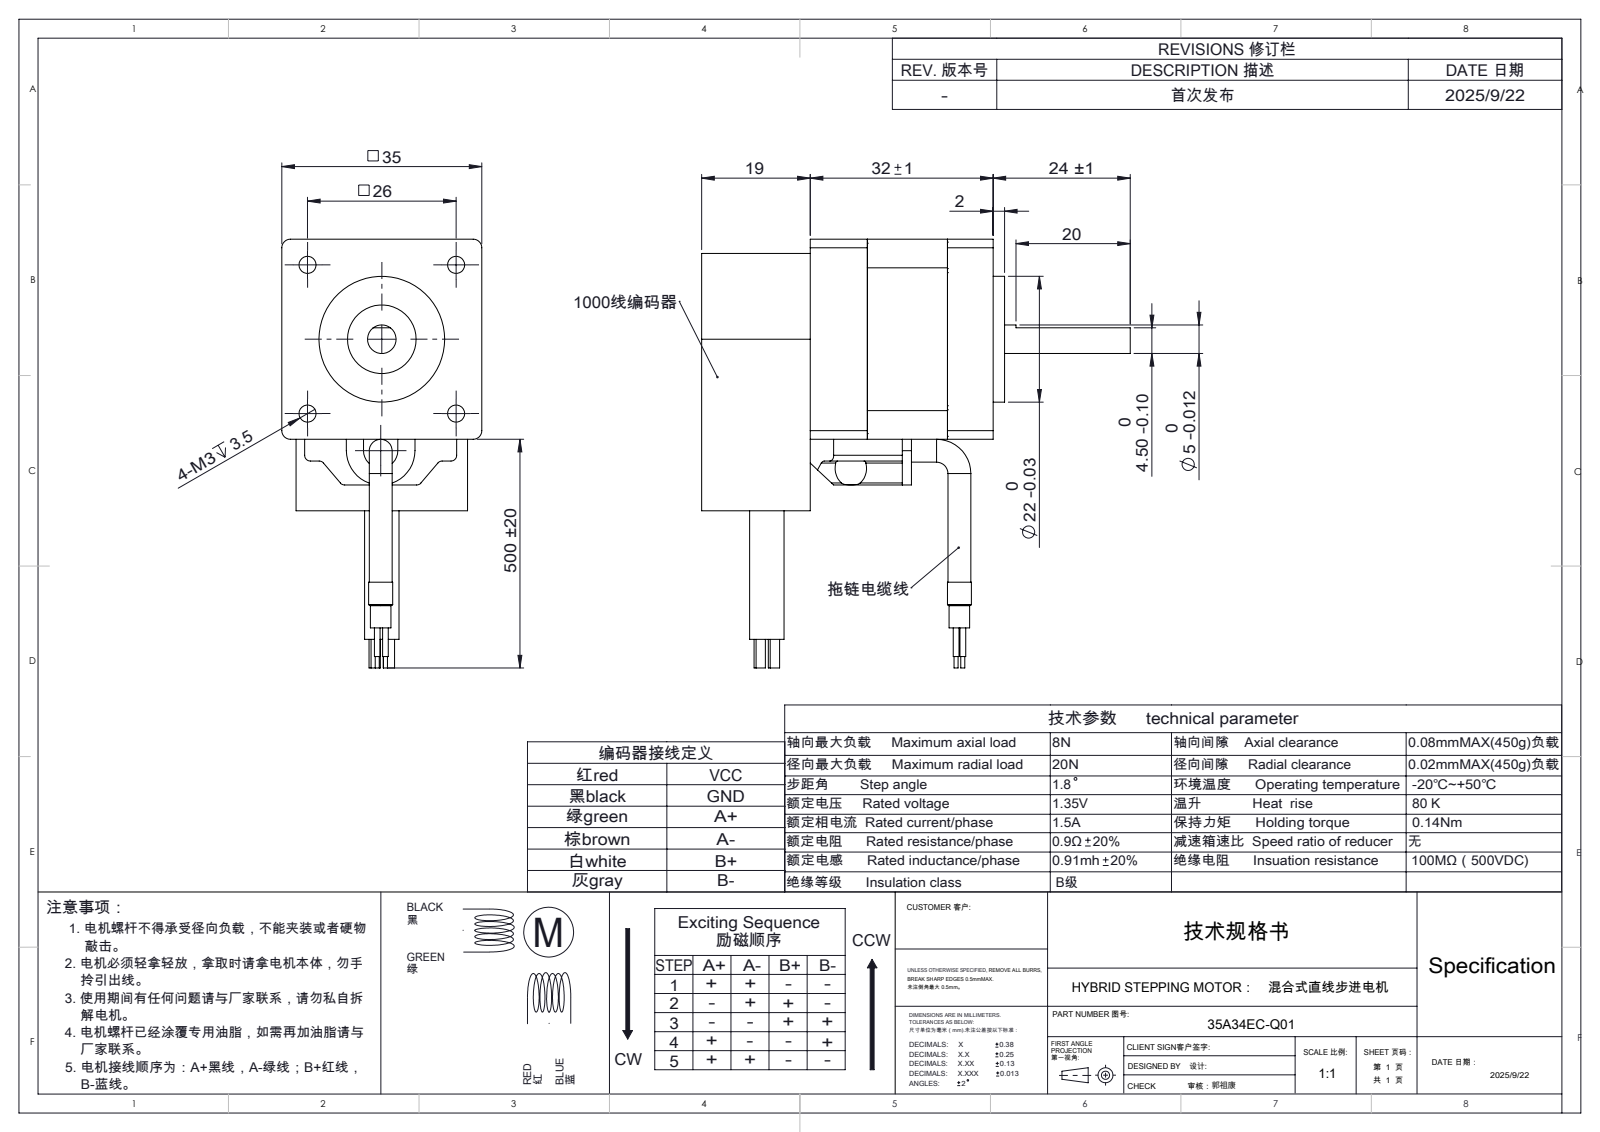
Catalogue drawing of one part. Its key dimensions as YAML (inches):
part_name: "35A34EC-Q01"
step_written_by: "SolidWorks 2024 (AUTOMOTIVE_DESIGN)"
units: inches
bodies: {solids: 5, faces: 182, planar: 74, cylindrical: 102, other: 6}
overall_size: [2.953, 2.953, 1.378]
volume: 3.772
surface_area: 28.7
round_holes:
  - {diameter: 0.118, count: 4}
  - {diameter: 0.126, count: 2}
  - {diameter: 0.217, count: 2}
  - {diameter: 0.472, count: 1}
round_bosses_or_shafts:
  - {diameter: 0.064, count: 4}
  - {diameter: 0.039, count: 4}
  - {diameter: 0.028, count: 4}
  - {diameter: 0.157, count: 2}
  - {diameter: 1.337, count: 1}
  - {diameter: 1.322, count: 1}
  - {diameter: 0.866, count: 1}
  - {diameter: 0.236, count: 1}
partial_cylinders:
  - {radius: 0.039, count: 6}
  - {radius: 0.059, count: 4}
  - {radius: 0.118, count: 1}
  - {radius: 0.191, count: 1}
  - {radius: 0.236, count: 1}
  - {radius: 0.591, count: 1}
  - {radius: 0.846, count: 1}
face_to_face_distances: [1.378, 0.748, 0.098, 1.28, 1.26, 0.394, 2.008, 0.945, 0.315, 1.693]
hole_center_spacings: [0.724, 1.024, 1.448, 0.728]
